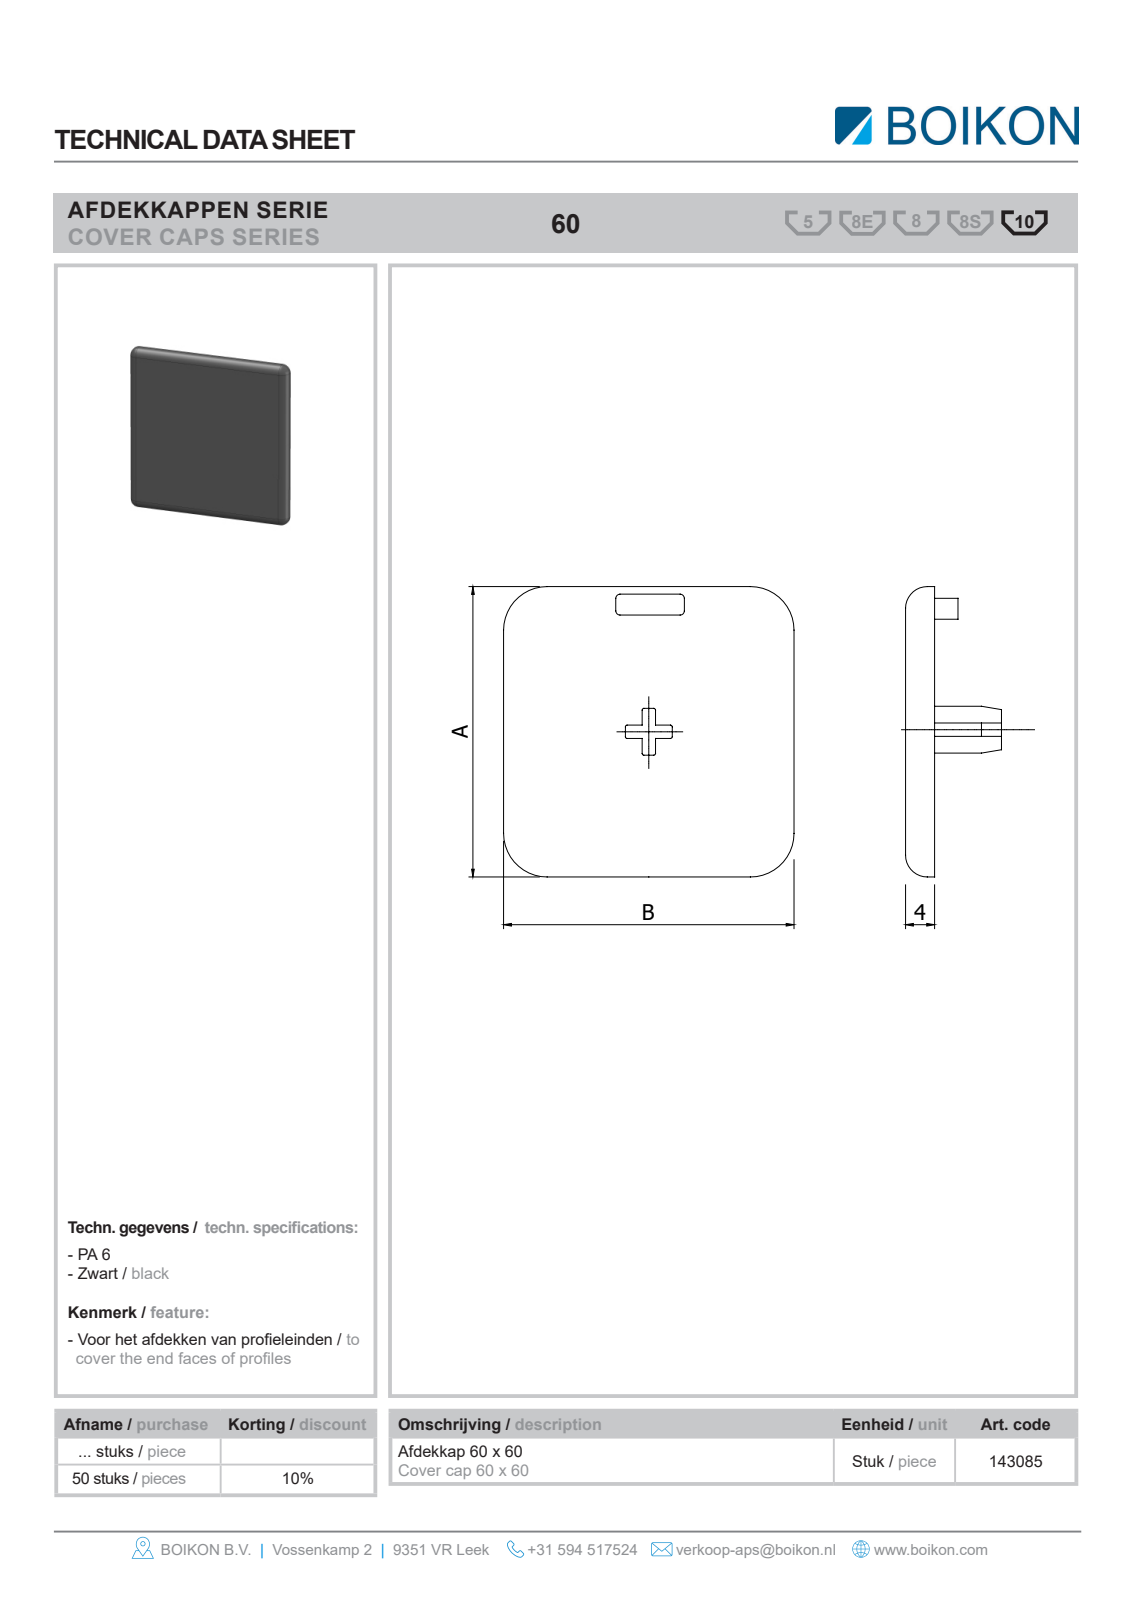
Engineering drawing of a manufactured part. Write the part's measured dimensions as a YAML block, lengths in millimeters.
part_name: "Root; 143085 Afdekkap 60 x 60BOIKON"
step_written_by: "HiCAD 2013 1802.4 Build 509 (AUTOMOTIVE_DESIGN)"
units: millimeters
bodies: {solids: 1, faces: 18, planar: 6, cylindrical: 8, other: 4}
overall_size: [60, 60, 4]
volume: 13924
surface_area: 7818
partial_cylinders:
  - {radius: 3, count: 8}
face_to_face_distances: [4, 60]
